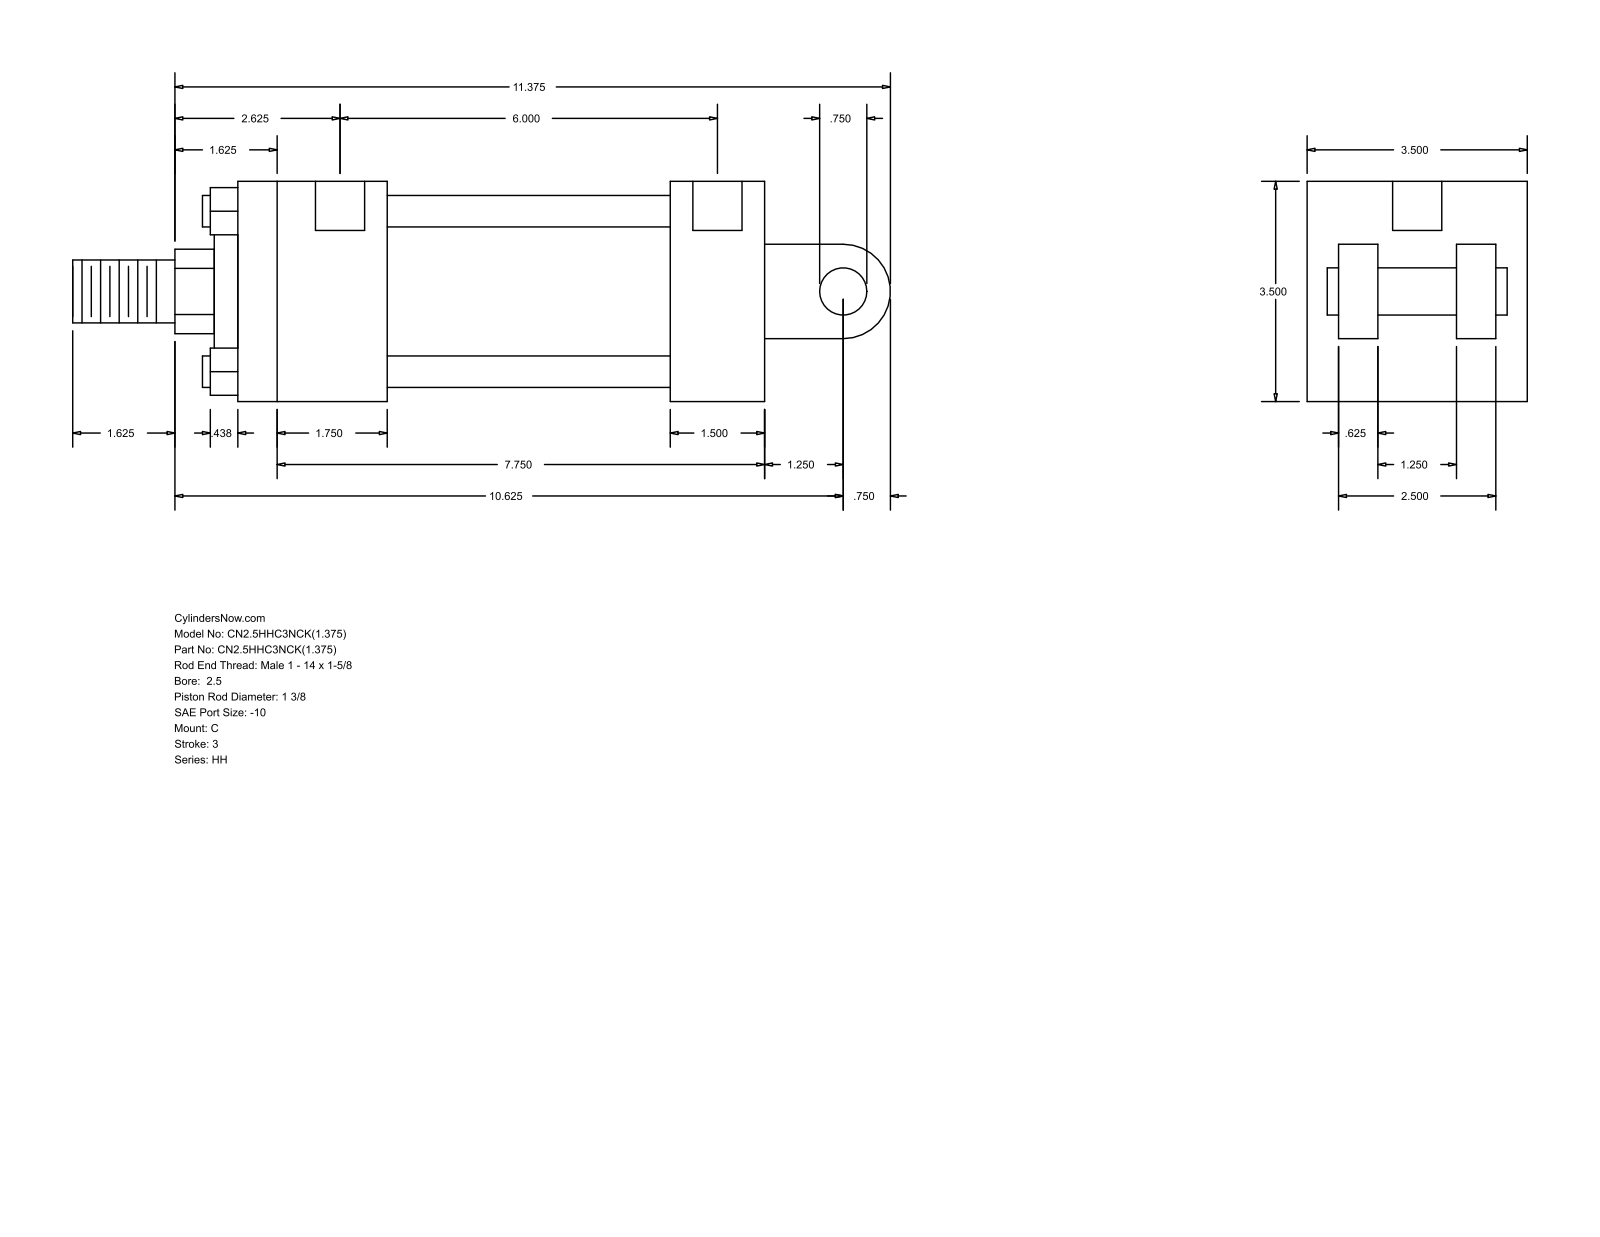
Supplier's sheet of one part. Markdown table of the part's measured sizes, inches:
| quantity | value |
| --- | --- |
| part name | HH_C__0250_1.375 |
| STEP written by | GSSL Pune (CONFIG_CONTROL_DESIGN) |
| units | inches |
| bodies | 0 solids, 99 faces (70 planar, 29 cylindrical, 0 other) |
| overall size | 13 × 3.5 × 3.5 |
| round holes (diameter × count) | 0.219 × 4, 0.781 × 2 |
| round bosses / shafts (diameter × count) | 0.5 × 4, 2.875 × 1, 2 × 1, 1.375 × 1, 1 × 1, 0.75 × 1 |
| partial cylindrical surfaces (radius × count) | 0.672 × 1, 0.75 × 1 |
| main face-to-face distances | 3.5, 8.375, 2.5, 0.5, 6.875, 1.5, 2.375, 4.5, 6, 3 |
| hole center spacings | 6.125, 0.062, 0.063, 6, 6.062, 6.063 |
